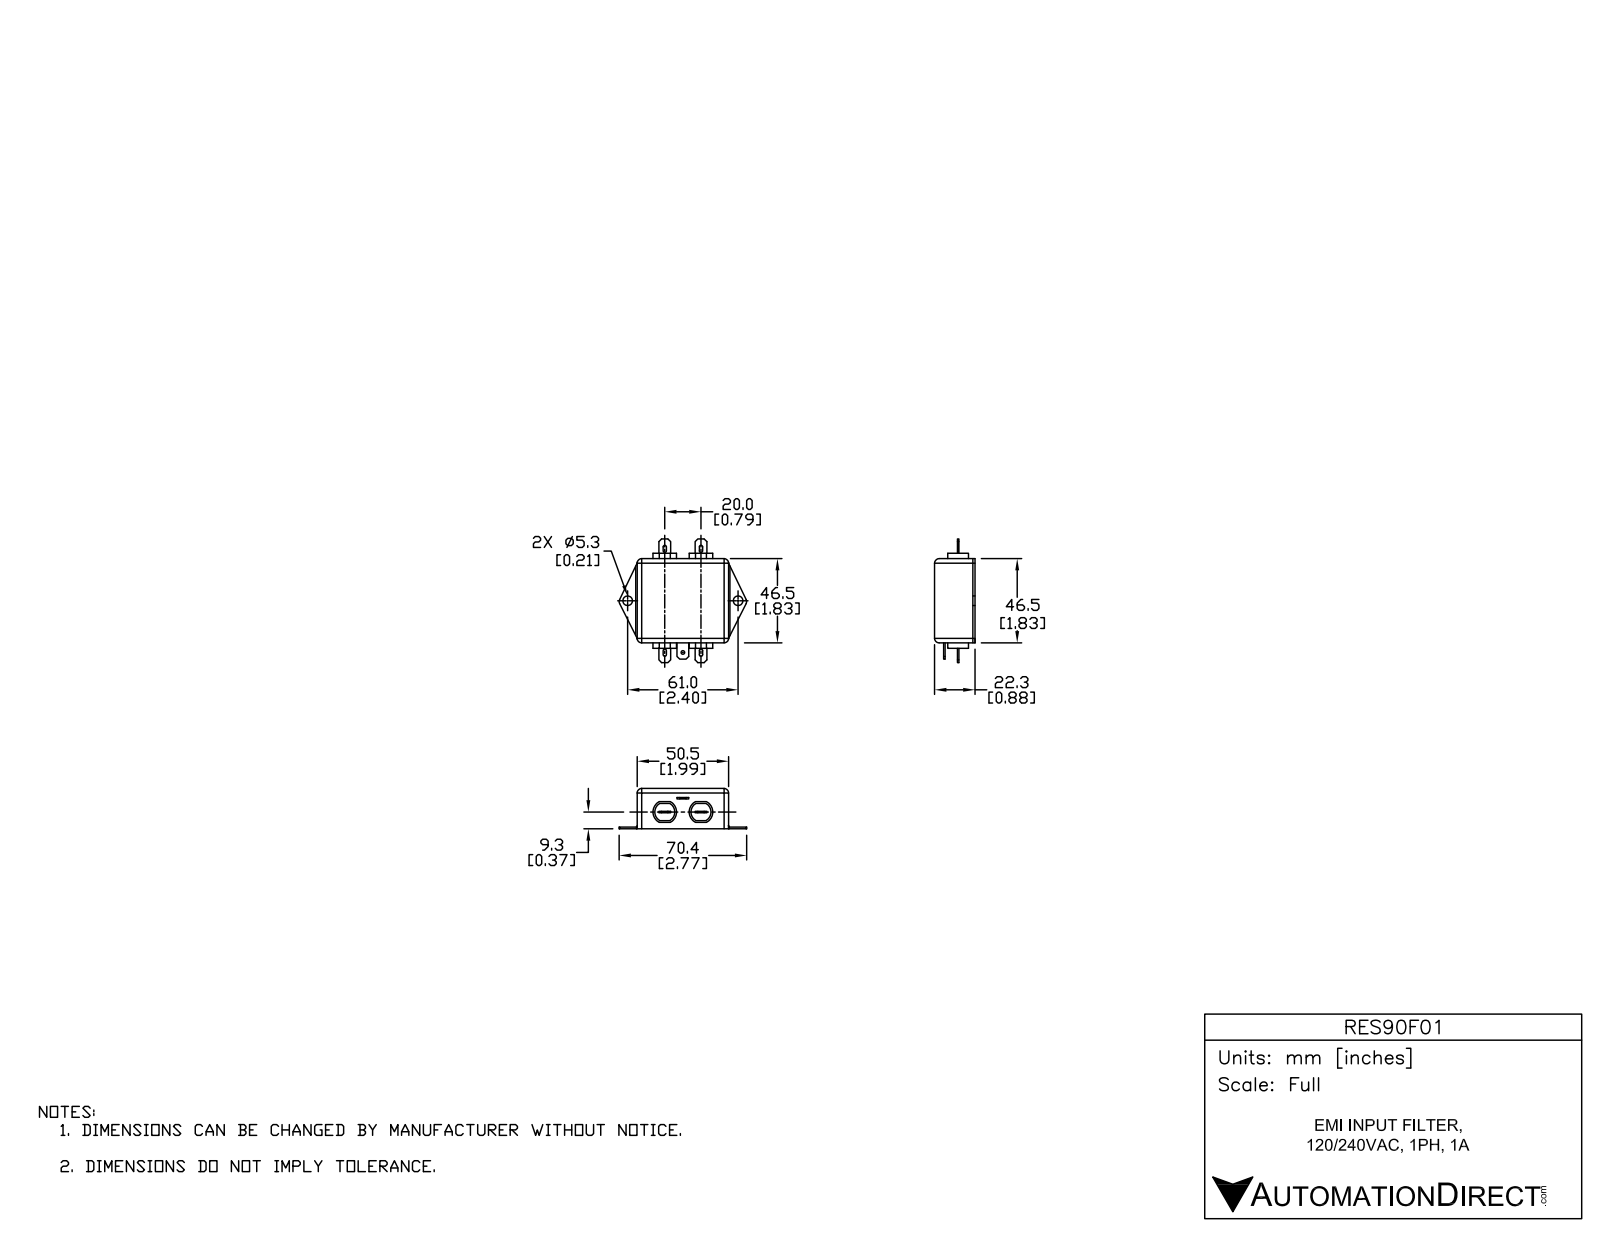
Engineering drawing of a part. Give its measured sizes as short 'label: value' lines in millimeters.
name: RES90F01
written by: SolidWorks 2015 (AUTOMOTIVE_DESIGN)
unit: mm
bodies: 1 solid, 137 faces (79 planar, 54 cylindrical, 4 other)
size: 70.42 × 68.3 × 22.3
volume: 53 546 mm³; area: 10 826 mm²
holes: 2× ⌀5.3, 1× ⌀2
rounds: 10× R2.5, 8× R0.9, 2× R0.75, 2× R5.5, 2× R6.5
face distances: 22.3, 50.5, 46.5, 1, 1.4, 47.9, 21.3, 0.8, 7.9, 8.9
hole spacings: 41.78, 61
